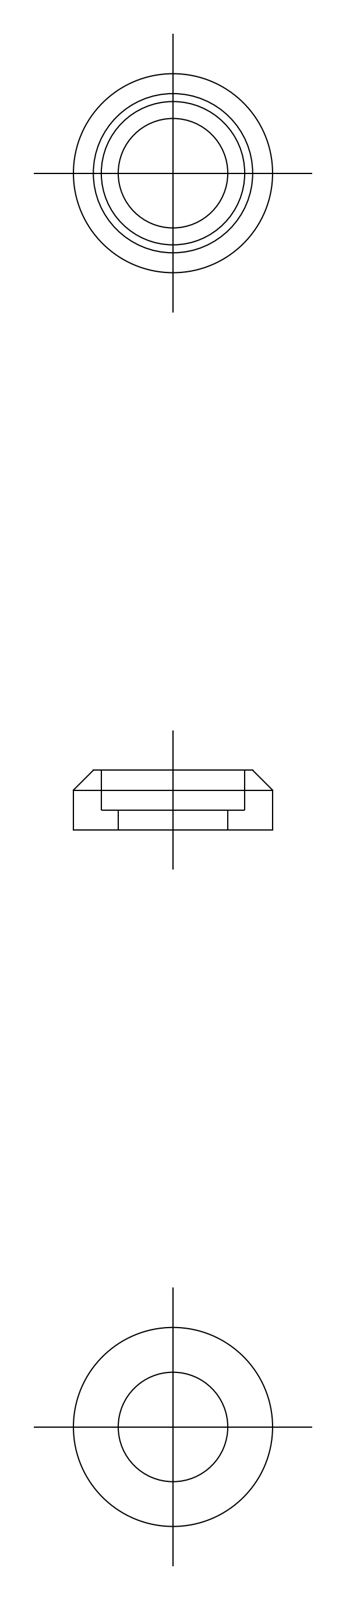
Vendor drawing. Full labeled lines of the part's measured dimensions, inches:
Part name (STEP PRODUCT): facing ring
STEP written by: CADfix (AUTOMOTIVE_DESIGN)
Units: inches
Bodies: 1 solid, 11 faces (0 planar, 0 cylindrical, 11 other)
Overall size (bounding box): 0.394 × 0.394 × 0.118
Volume: 0.007 in³ · Surface area: 0.383 in²
